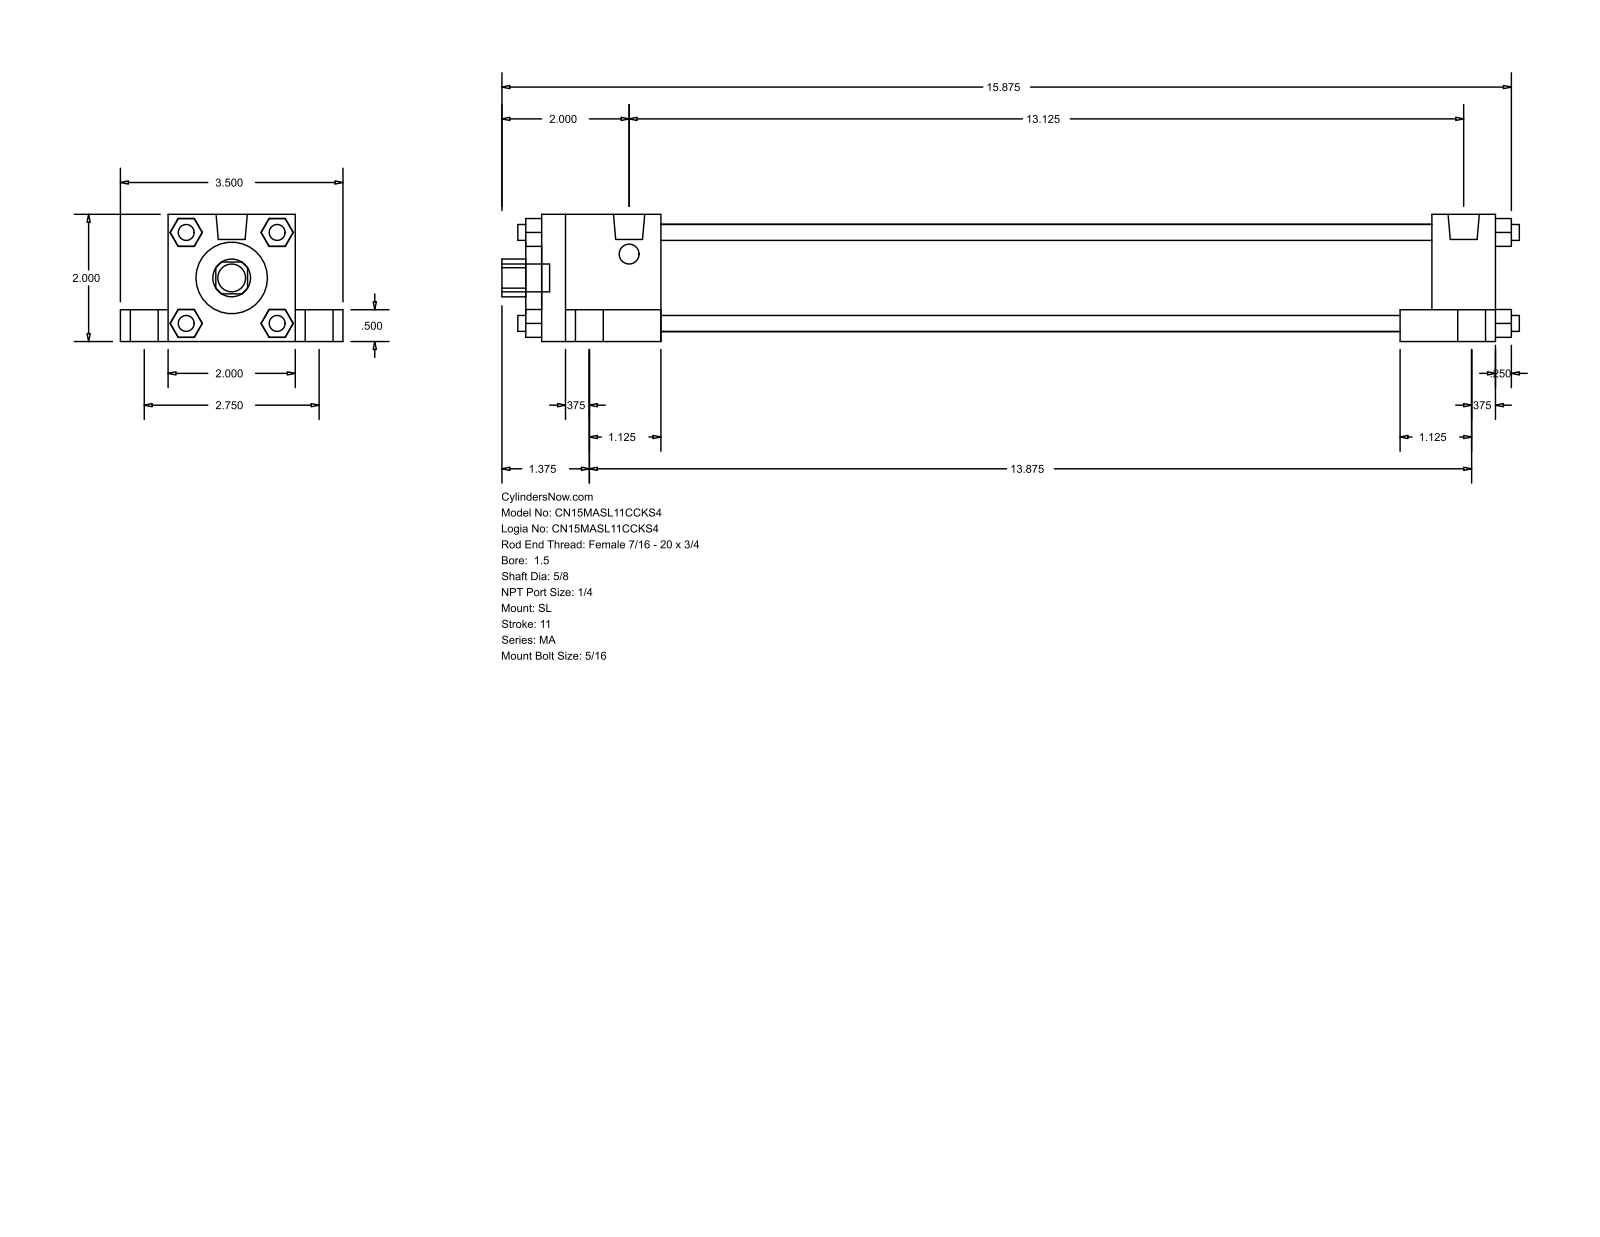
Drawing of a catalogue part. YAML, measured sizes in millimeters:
part_name: "MA_SL__0150_0.625"
step_written_by: "GSSL Pune (CONFIG_CONTROL_DESIGN)"
units: millimeters
bodies: {solids: 0, faces: 148, planar: 112, cylindrical: 36, other: 0}
overall_size: [406.4, 88.9, 50.8]
round_holes:
  - {diameter: 15.88, count: 1}
  - {diameter: 28.57, count: 1}
  - {diameter: 42.93, count: 1}
round_bosses_or_shafts:
  - {diameter: 11.11, count: 5}
  - {diameter: 17.46, count: 4}
  - {diameter: 7.94, count: 4}
  - {diameter: 6.35, count: 4}
  - {diameter: 12.49, count: 2}
partial_cylinders:
  - {radius: 7.54, count: 1}
face_to_face_distances: [50.8, 19.05, 38.1, 12.7, 381, 69.85, 9.52, 6.35, 387.35, 25.4]
